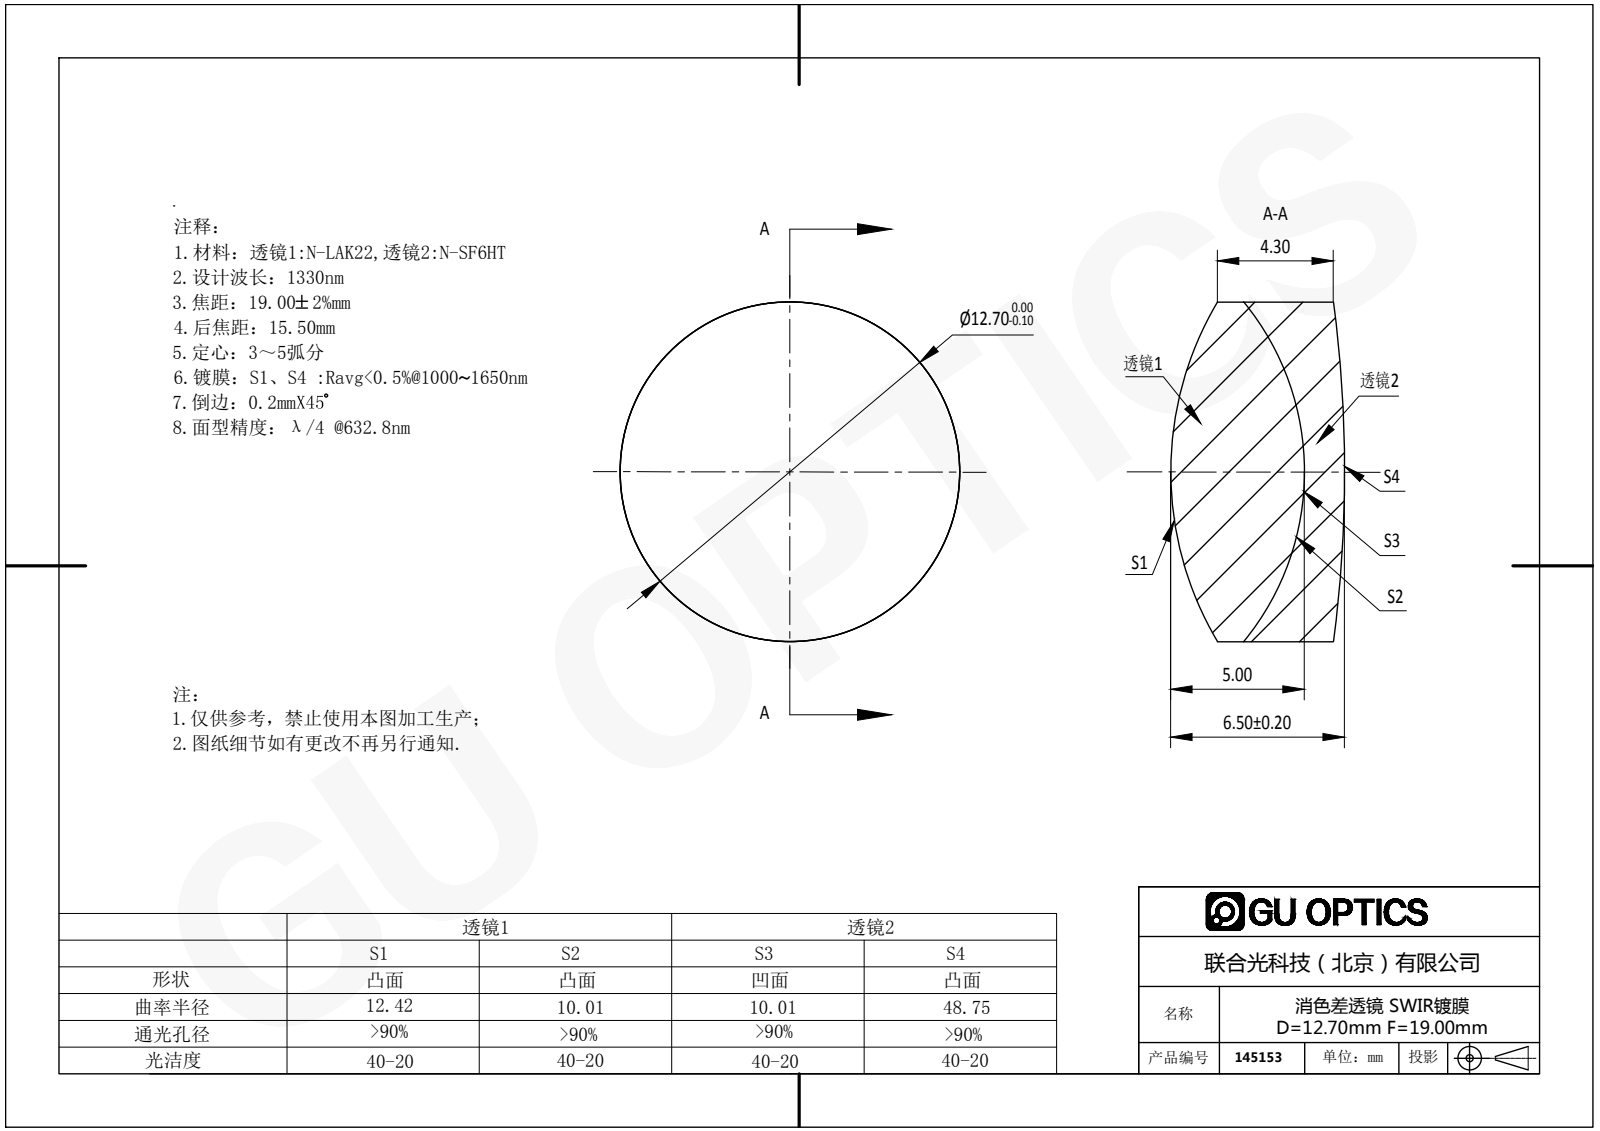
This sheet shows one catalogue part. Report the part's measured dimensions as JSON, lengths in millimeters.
{"part_name": "145153", "step_written_by": "SolidWorks 2016 (AUTOMOTIVE_DESIGN)", "units": "millimeters", "bodies": {"solids": 2, "faces": 12, "planar": 0, "cylindrical": 4, "other": 8}, "overall_size": [12.7, 12.7, 6.5], "volume_mm3": 689, "surface_area_mm2": 722, "round_bosses_or_shafts": [[12.7, 1]]}
